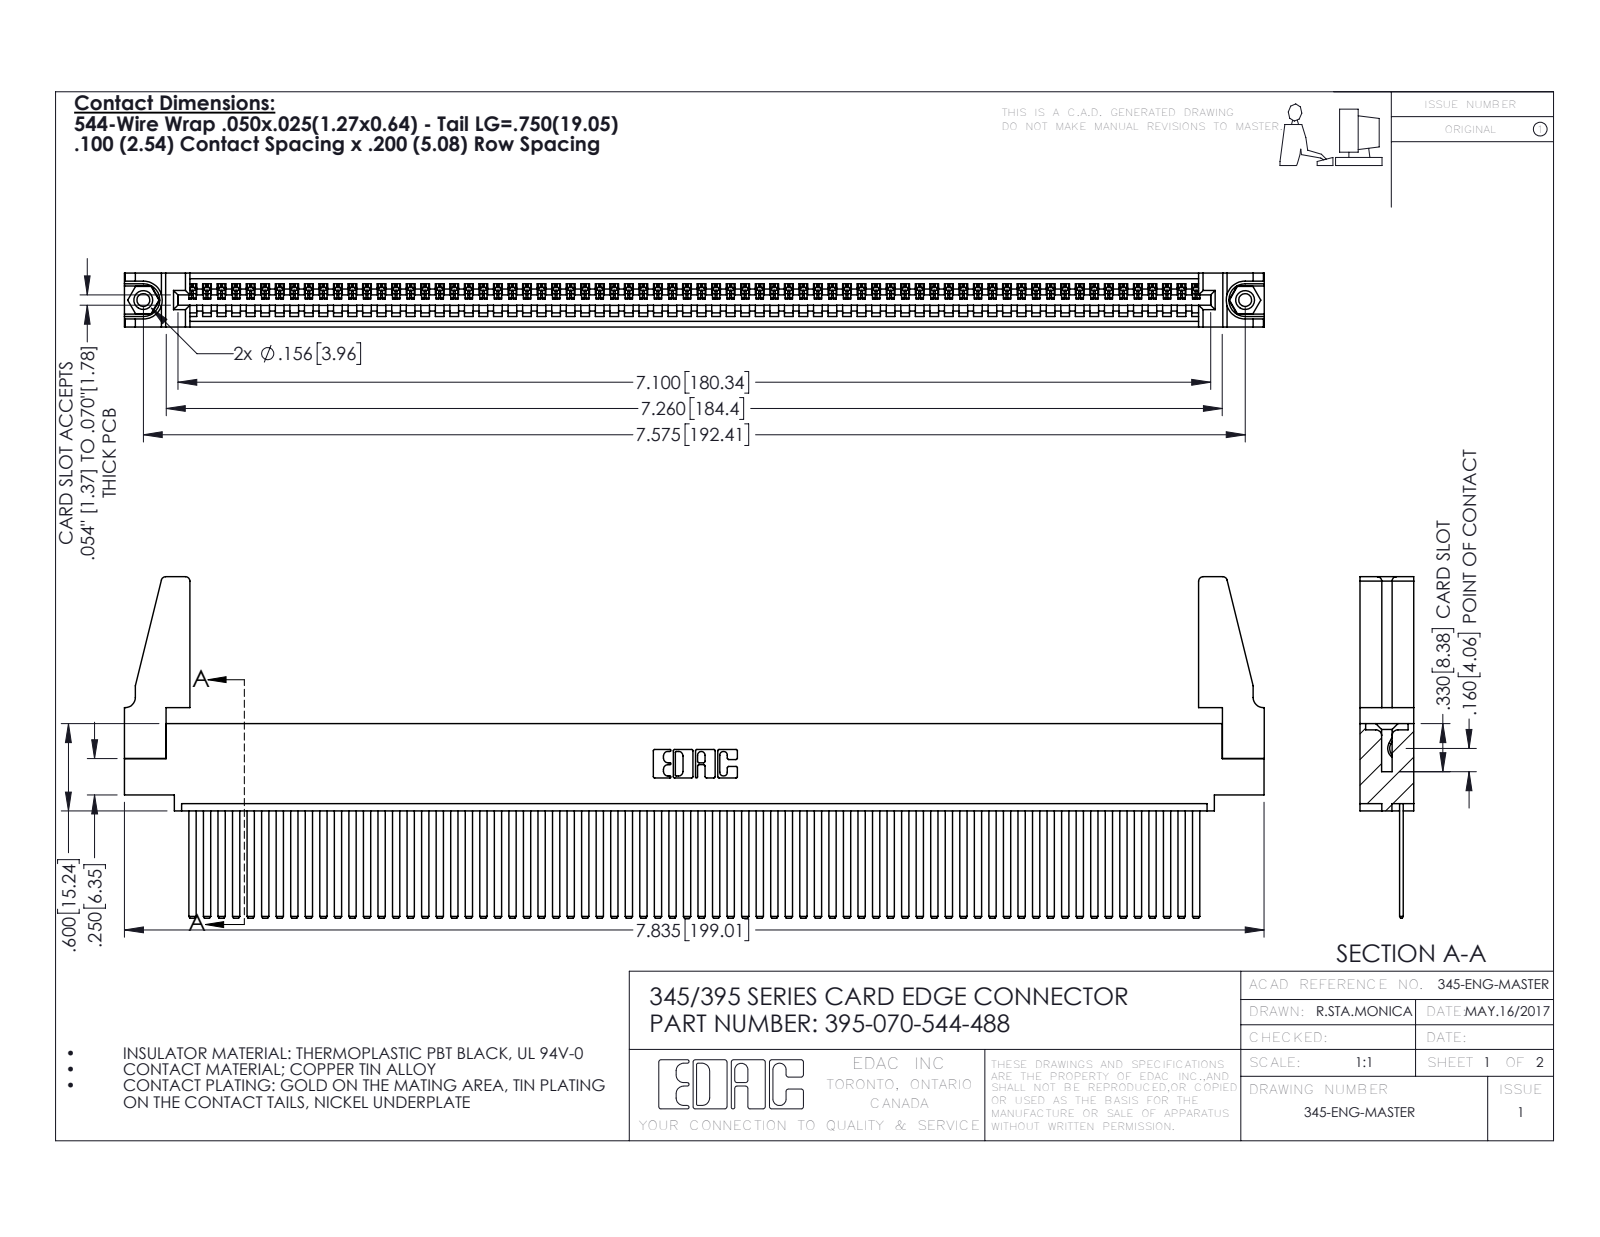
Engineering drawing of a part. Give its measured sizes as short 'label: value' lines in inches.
name: 345 Part_0.110 Offset - 0.156 Dia-TH; 345-250-001_345-250-001-102; 395-070-544-488; 345-220-078_345-220-088 (+1 more)
written by: SolidWorks 2016 (CONFIG_CONTROL_DESIGN)
unit: in
bodies: 75 solids, 3894 faces (2676 planar, 1202 cylindrical, 16 other)
size: 7.836 × 2.347 × 0.37
volume: 1.411 in³; area: 50.27 in²
holes: 2× ⌀0.089, 2× ⌀0.125, 2× ⌀0.156, 1× ⌀0.064
bosses: 2× ⌀0.155
rounds: 140× R0.006, 22× R0.01, 8× R0.03, 6× R0.007, 6× R0.031, 3× R0.026, 2× R0.031, 2× R0.04
face distances: 0.072, 0.298, 0.098, 0.272, 0.025, 0.37, 0.2, 0.225, 0.149, 0.072
hole spacings: 0.27, 7.339, 7.575
